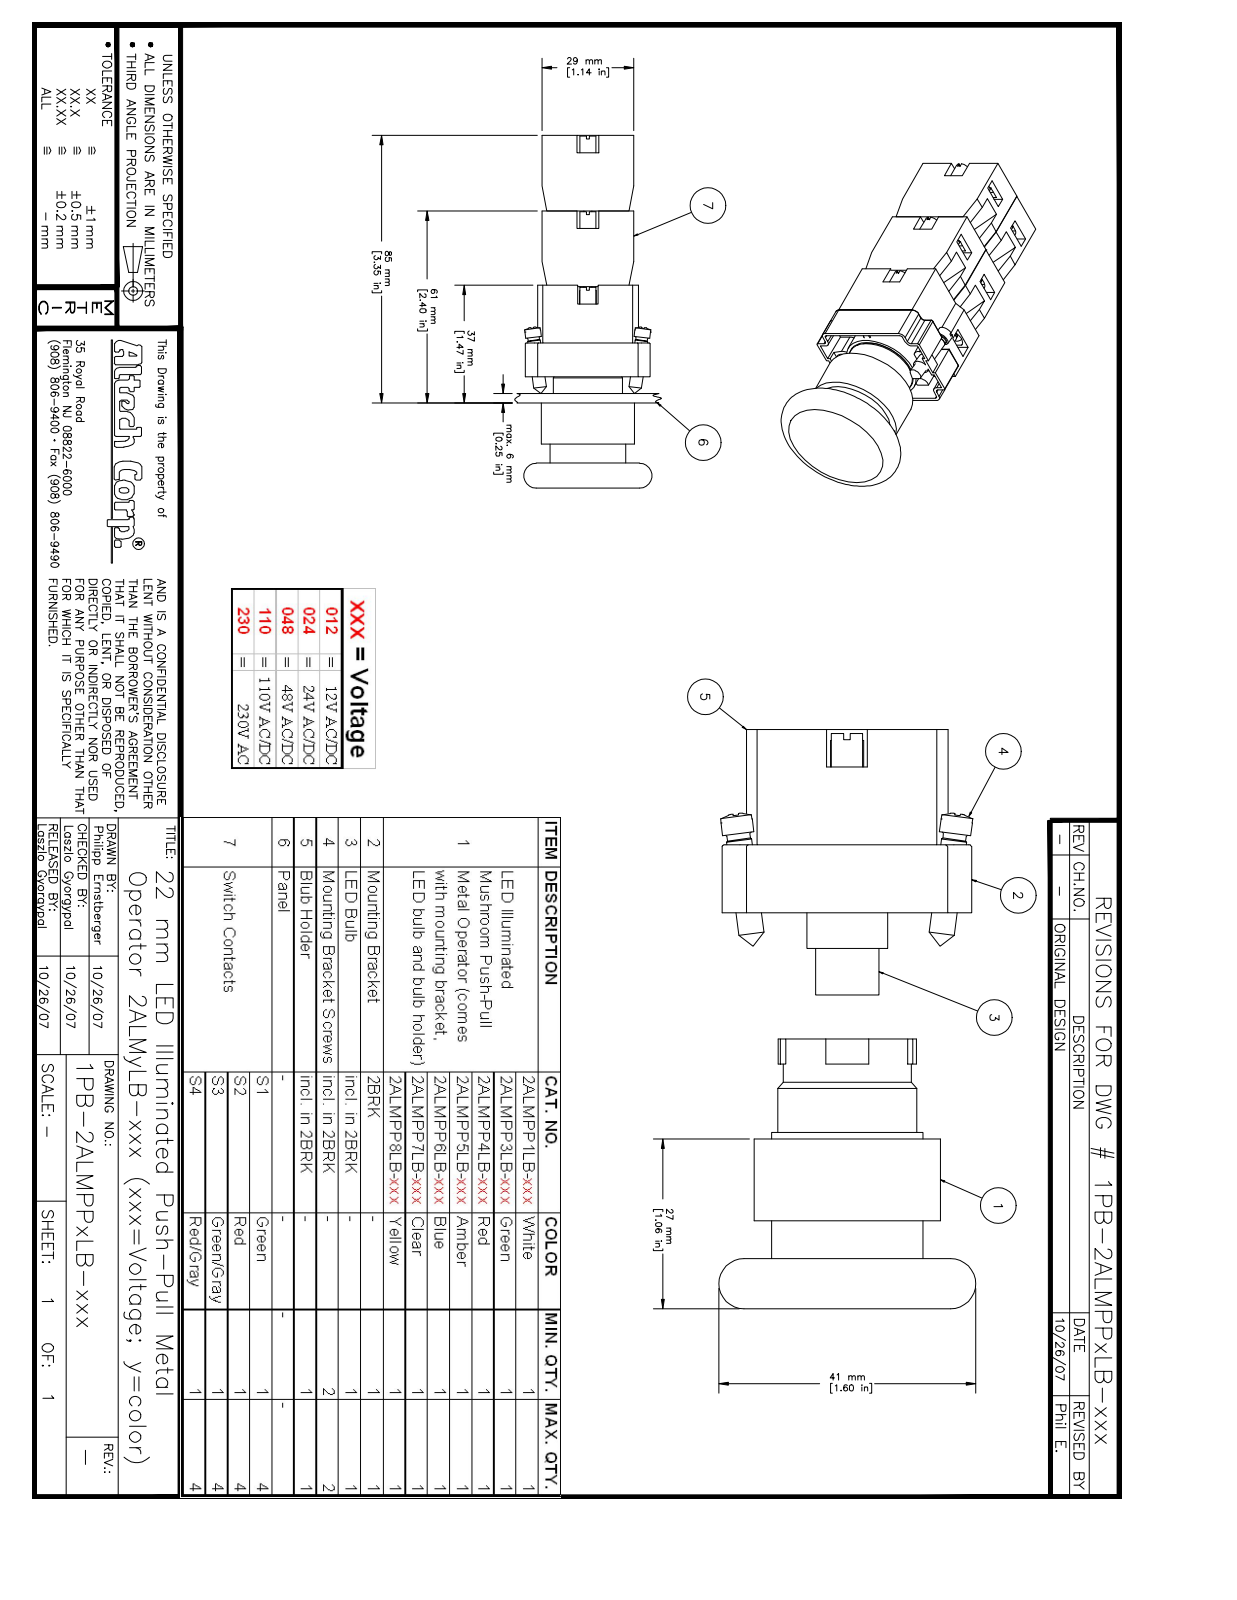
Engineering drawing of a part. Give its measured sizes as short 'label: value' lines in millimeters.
name: 2ALMPPxLB-xxx_assembly; 2ALMPPxLB-xxx; rubber_gasket; panel (+8 more)
written by: Autodesk Inventor 2008 (AUTOMOTIVE_DESIGN)
unit: mm
bodies: 28 solids, 1085 faces (588 planar, 180 cylindrical, 317 other)
size: 112 × 60.45 × 45
volume: 78 548 mm³; area: 50 367 mm²
holes: 5× ⌀2.5, 2× ⌀2.6, 1× ⌀13.5, 1× ⌀17.75, 1× ⌀22, 1× ⌀22.25, 1× ⌀22.5, 1× ⌀25.3, 1× ⌀27.5, 1× ⌀32.75
bosses: 8× ⌀3, 6× ⌀2.75, 4× ⌀5, 4× ⌀1.5, 2× ⌀4, 2× ⌀3.65, 1× ⌀29.5, 1× ⌀24.25
rounds: 14× R1, 10× R0.25, 8× R0.72, 5× R2.25, 4× R0.5, 4× R0.8, 4× R1.8, 4× R2
face distances: 14.8, 3, 14.7, 24, 19.1, 15.05, 14.95, 29.75, 30, 61
hole spacings: 14.53, 6.52, 6.57, 13, 25.88, 26, 26.27, 29.07
